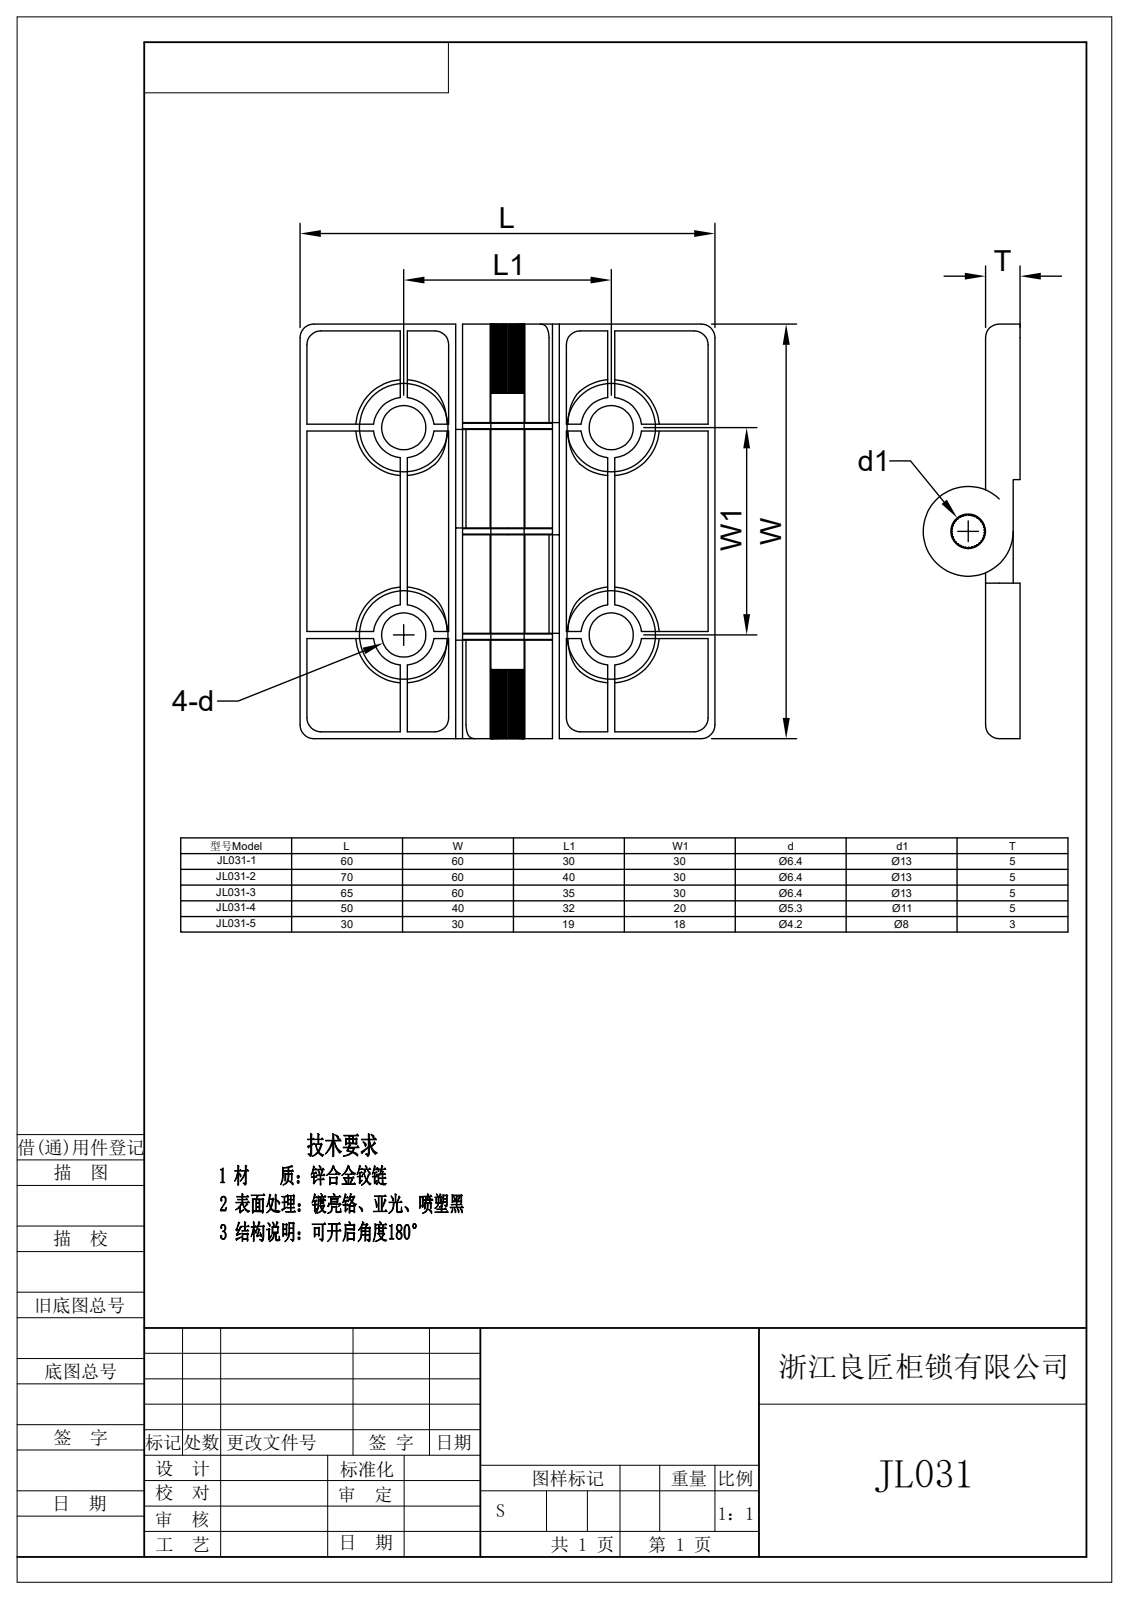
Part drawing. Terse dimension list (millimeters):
written by: Rhino 8.5 (CONFIG_CONTROL_DESIGN)
unit: mm
bodies: 28 solids, 1842 faces (934 planar, 728 cylindrical, 180 other)
size: 311.43 × 70 × 14
volume: 37 700 mm³; area: 59 926 mm²
holes: 1× ⌀3, 1× ⌀3.8, 1× ⌀4, 1× ⌀4.8, 1× ⌀5
bosses: 1× ⌀13, 1× ⌀11, 1× ⌀8, 1× ⌀2.8
rounds: 140× R0.1, 82× R2, 22× R1
face distances: 1, 4, 5, 3, 2.5, 60, 12, 17, 40, 76.34
hole spacings: 0.5, 1
